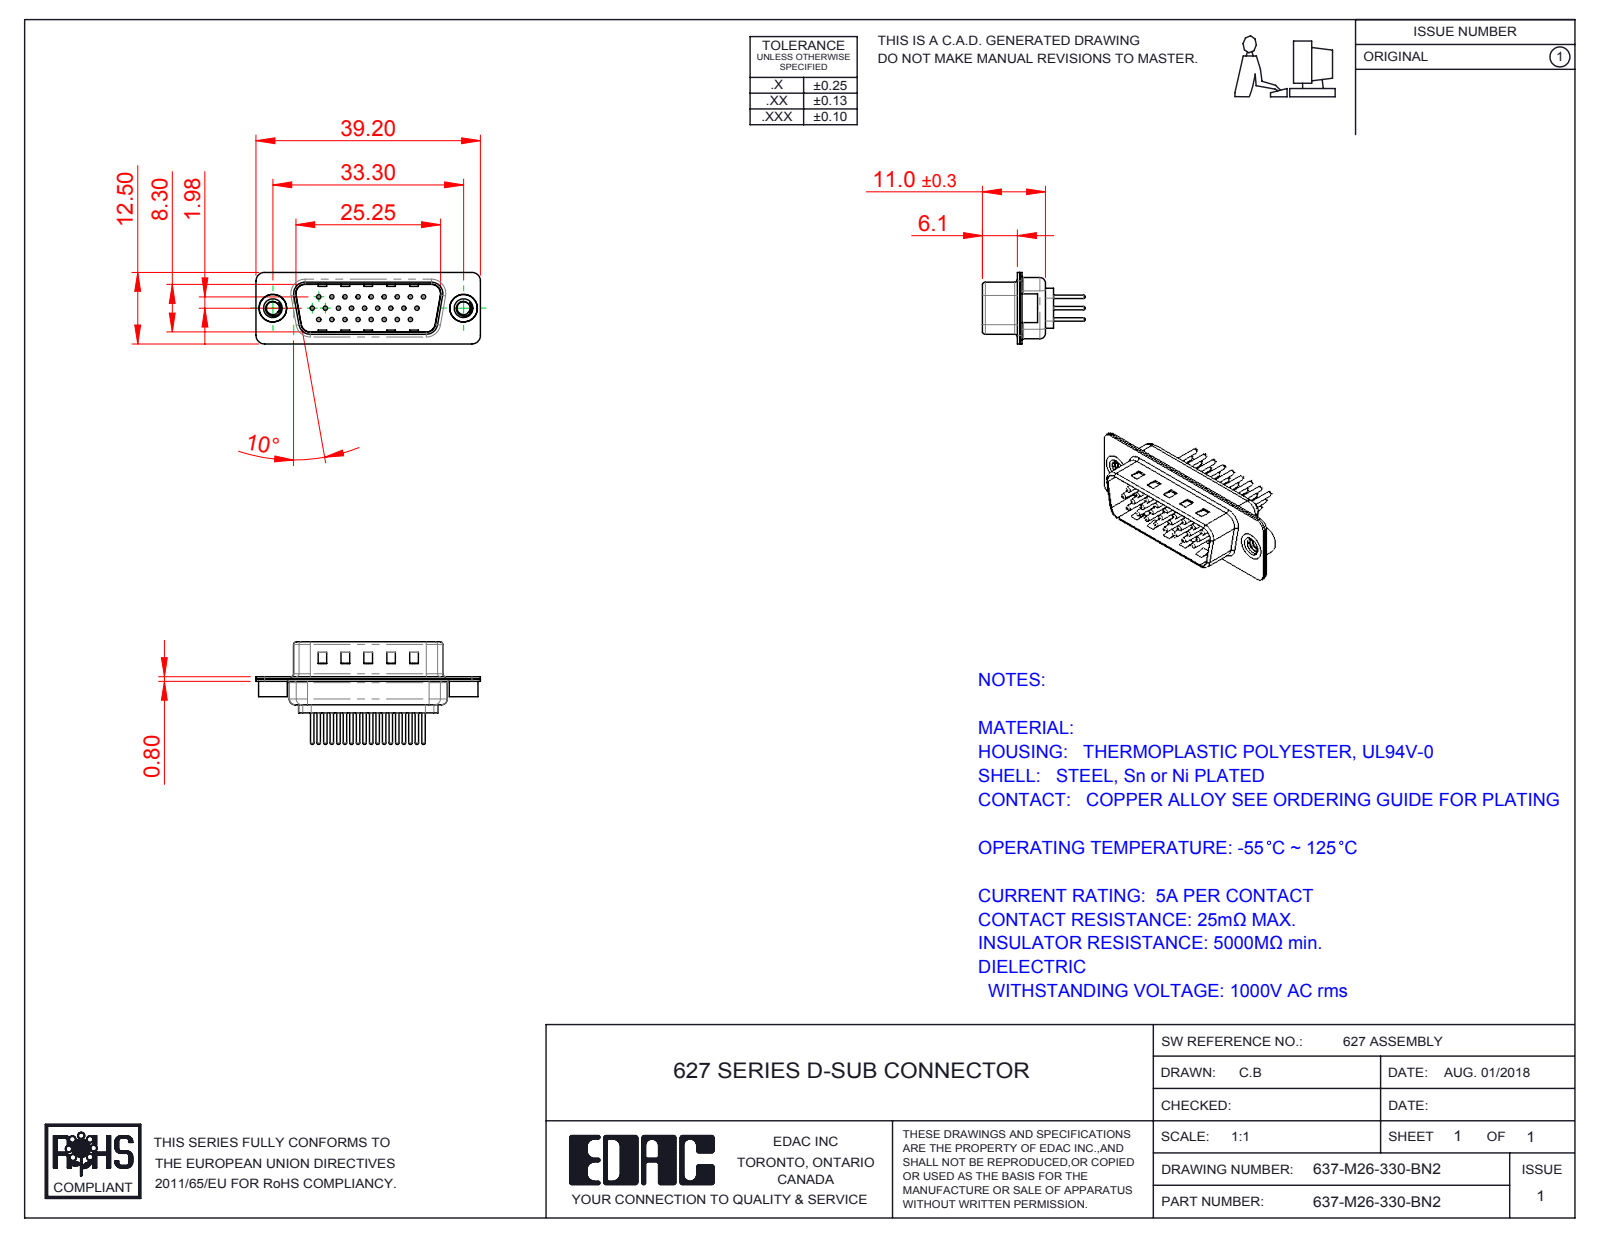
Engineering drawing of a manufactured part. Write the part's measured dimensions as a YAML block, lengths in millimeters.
part_name: "637M Contact Row 2_30; 637M Shell Rear_26 Contacts; 637M Contact Row 3_30; 637M 4-40 Threaded Rivet (+4 more)"
step_written_by: "SolidWorks 2016 (CONFIG_CONTROL_DESIGN)"
units: millimeters
bodies: {solids: 31, faces: 1302, planar: 321, cylindrical: 497, other: 484}
overall_size: [39.2, 17.9, 12.5]
volume: 1909
surface_area: 5751
round_holes:
  - {diameter: 0.75, count: 26}
  - {diameter: 1.6, count: 26}
  - {diameter: 2, count: 26}
  - {diameter: 2.26, count: 2}
  - {diameter: 4, count: 2}
  - {diameter: 4.8, count: 2}
round_bosses_or_shafts:
  - {diameter: 1.5, count: 26}
  - {diameter: 0.6, count: 26}
  - {diameter: 5, count: 2}
  - {diameter: 4.9, count: 2}
partial_cylinders:
  - {radius: 1.5, count: 16}
  - {radius: 2, count: 12}
  - {radius: 0.5, count: 8}
  - {radius: 1.6, count: 8}
  - {radius: 0.25, count: 4}
  - {radius: 0.6, count: 4}
  - {radius: 0.65, count: 4}
  - {radius: 0.9, count: 4}
face_to_face_distances: [0.4, 0.8, 9.5, 9.1, 8.7, 9.9, 0.75, 5.5, 0.35, 5.9]
hole_center_spacings: [3.96, 2.28, 4.57, 6.05, 2.29, 8.24, 6.86, 10.48]
